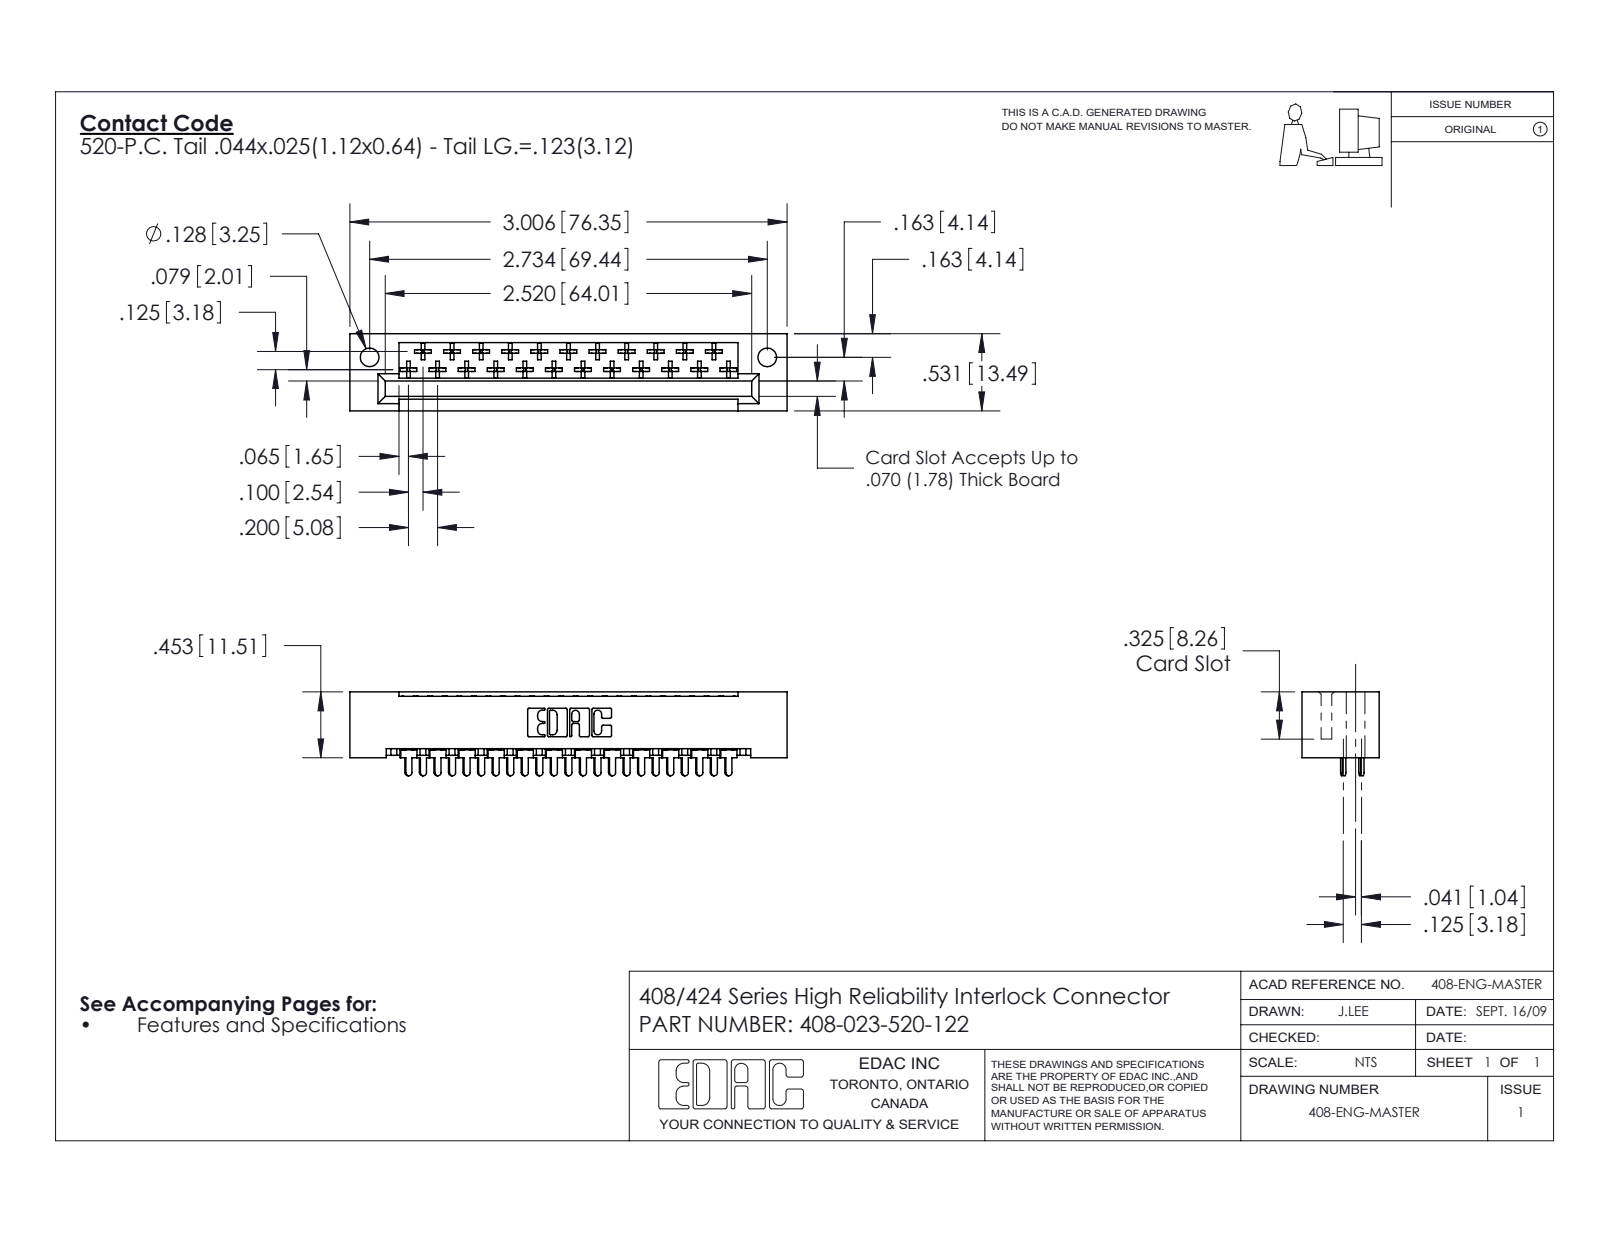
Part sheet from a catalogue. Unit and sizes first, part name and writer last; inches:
Units: inches
Overall size (bounding box): 3.006 × 0.576 × 0.531
Round holes (diameter × count): ⌀0.128 ×2
Partial cylindrical surfaces — rounded edges, fillets, slot ends (radius × count): R0.01 ×138, R0.02 ×25, R0.022 ×23, R0.01 ×22, R0.007 ×6, R0.031 ×6, R0.026 ×3
Main face-to-face distances: 0.1, 0.296, 0.531, 0.025, 0.125, 0.025, 0.272, 0.235, 0.259, 0.217
Hole centre spacings: 2.734
Volume: 0.517 in³ · Surface area: 15.56 in²
Bodies: 24 solids, 1392 faces (1045 planar, 255 cylindrical, 92 other)
Part name (STEP PRODUCT): 408-023-520-122; 408-290-001_408-290-120; 408 Part_023 - 1
STEP written by: SolidWorks 2016 (CONFIG_CONTROL_DESIGN)
